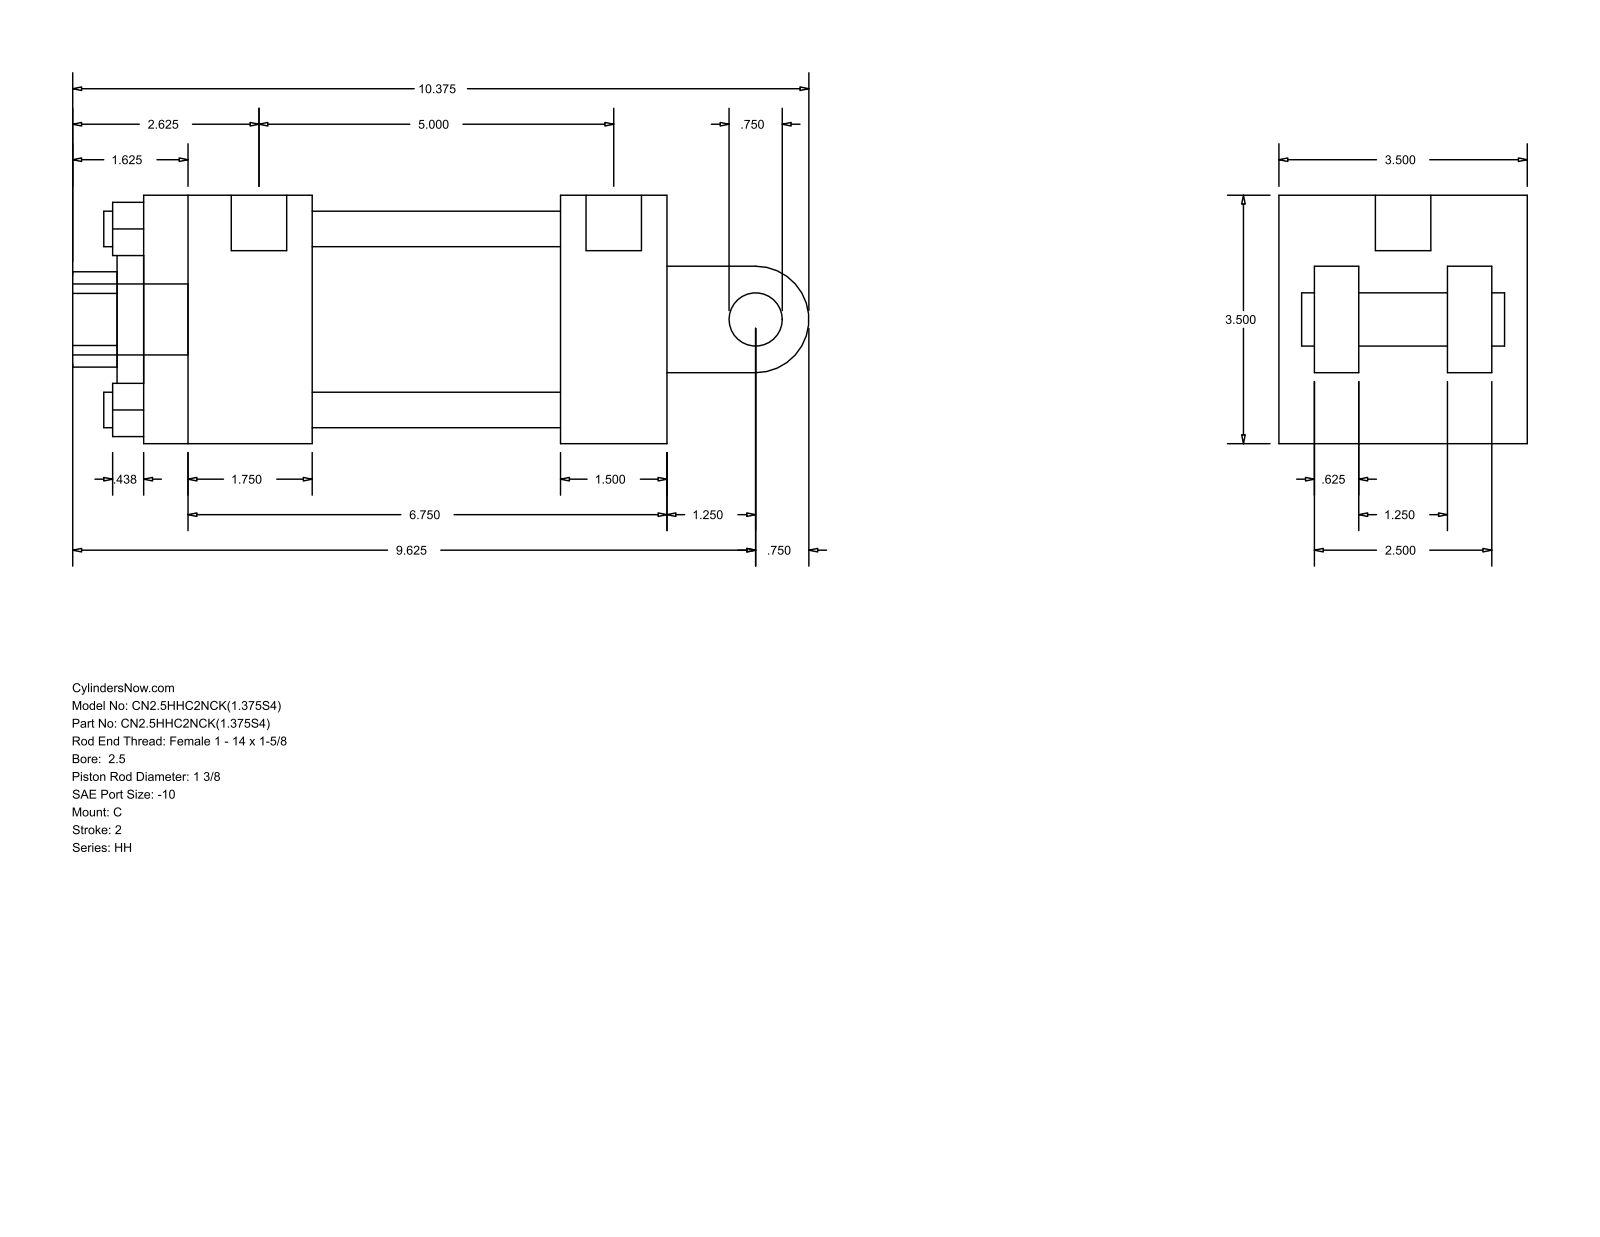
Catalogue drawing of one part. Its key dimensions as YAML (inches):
part_name: "HH_C__0250_1.375"
step_written_by: "GSSL Pune (CONFIG_CONTROL_DESIGN)"
units: inches
bodies: {solids: 0, faces: 99, planar: 70, cylindrical: 29, other: 0}
overall_size: [10.375, 3.5, 3.5]
round_holes:
  - {diameter: 0.5, count: 4}
  - {diameter: 0.219, count: 2}
  - {diameter: 0.781, count: 1}
  - {diameter: 1.375, count: 1}
  - {diameter: 2, count: 1}
  - {diameter: 2.875, count: 1}
round_bosses_or_shafts:
  - {diameter: 0.219, count: 2}
  - {diameter: 1, count: 1}
  - {diameter: 0.781, count: 1}
  - {diameter: 0.75, count: 1}
partial_cylinders:
  - {radius: 0.672, count: 1}
  - {radius: 0.75, count: 1}
face_to_face_distances: [3.5, 7.375, 1.5, 2.5, 0.625, 0.5, 5.875, 2.375, 5, 1.125]
hole_center_spacings: [1.803, 2.55, 3.606, 0.062]
